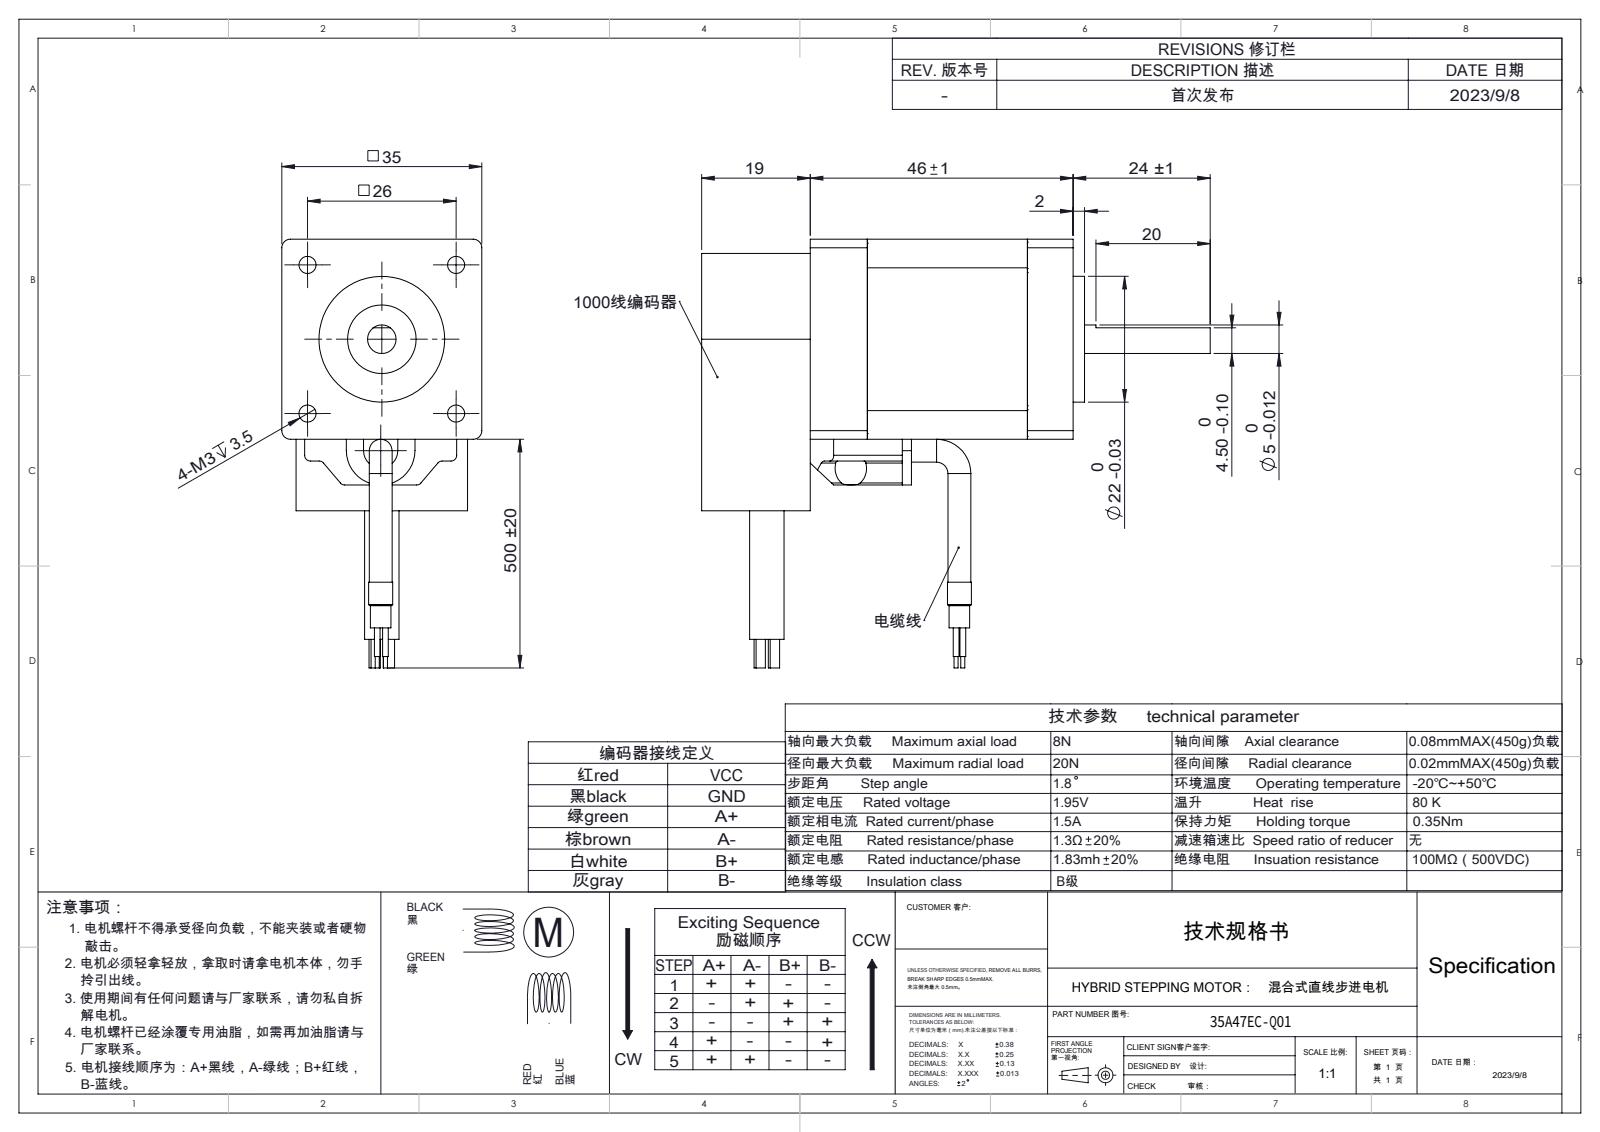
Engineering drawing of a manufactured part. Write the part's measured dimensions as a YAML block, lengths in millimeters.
part_name: "35HS247-1504E-XXX"
step_written_by: "SolidWorks 2020 (AUTOMOTIVE_DESIGN)"
units: millimeters
bodies: {solids: 5, faces: 182, planar: 74, cylindrical: 102, other: 6}
overall_size: [89, 75, 35]
volume: 76350
surface_area: 21371
round_holes:
  - {diameter: 3, count: 4}
  - {diameter: 3.2, count: 2}
  - {diameter: 5.5, count: 2}
  - {diameter: 12, count: 1}
round_bosses_or_shafts:
  - {diameter: 1.63, count: 4}
  - {diameter: 1, count: 4}
  - {diameter: 0.7, count: 4}
  - {diameter: 4, count: 2}
  - {diameter: 33.95, count: 1}
  - {diameter: 33.58, count: 1}
  - {diameter: 22, count: 1}
  - {diameter: 6, count: 1}
partial_cylinders:
  - {radius: 1, count: 6}
  - {radius: 1.5, count: 4}
  - {radius: 3, count: 1}
  - {radius: 4.86, count: 1}
  - {radius: 6, count: 1}
  - {radius: 15, count: 1}
  - {radius: 21.5, count: 1}
face_to_face_distances: [35, 19, 2.5, 32.5, 10, 65, 46, 38, 8, 36]
hole_center_spacings: [18.38, 26, 36.77, 18.5]
